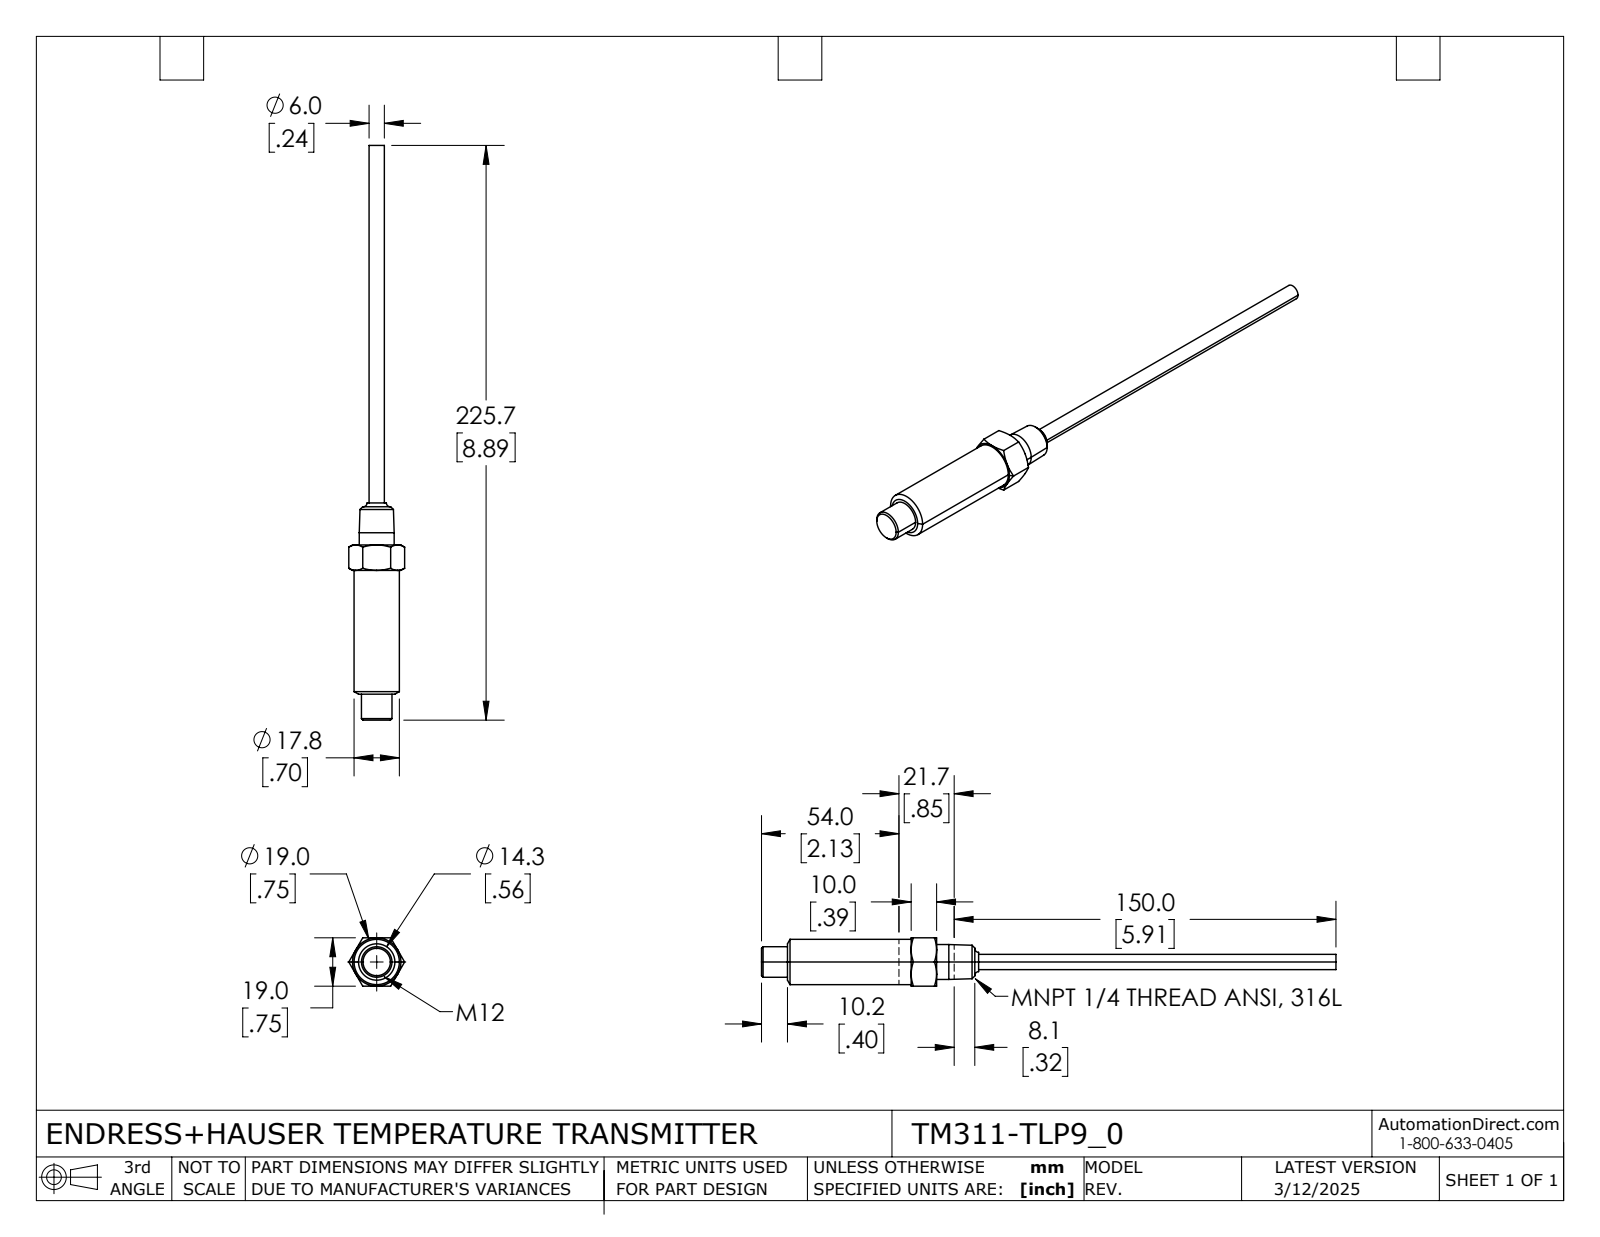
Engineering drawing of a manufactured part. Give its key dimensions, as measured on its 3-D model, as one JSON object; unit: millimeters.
{"part_name": "TM311-TLP9_0", "step_written_by": "SolidWorks 2021 (AUTOMOTIVE_DESIGN)", "units": "millimeters", "bodies": {"solids": 1, "faces": 47, "planar": 13, "cylindrical": 8, "other": 26}, "overall_size": [225.7, 21.9, 19], "volume_mm3": 22480, "surface_area_mm2": 7568, "round_bosses_or_shafts": [[17.8, 1], [13.7, 1], [12, 1], [6, 1]], "face_to_face_distances": [19, 68.8, 58.6, 10.2, 10, 48.6, 58.8, 156.9, 166.9, 215.5]}
